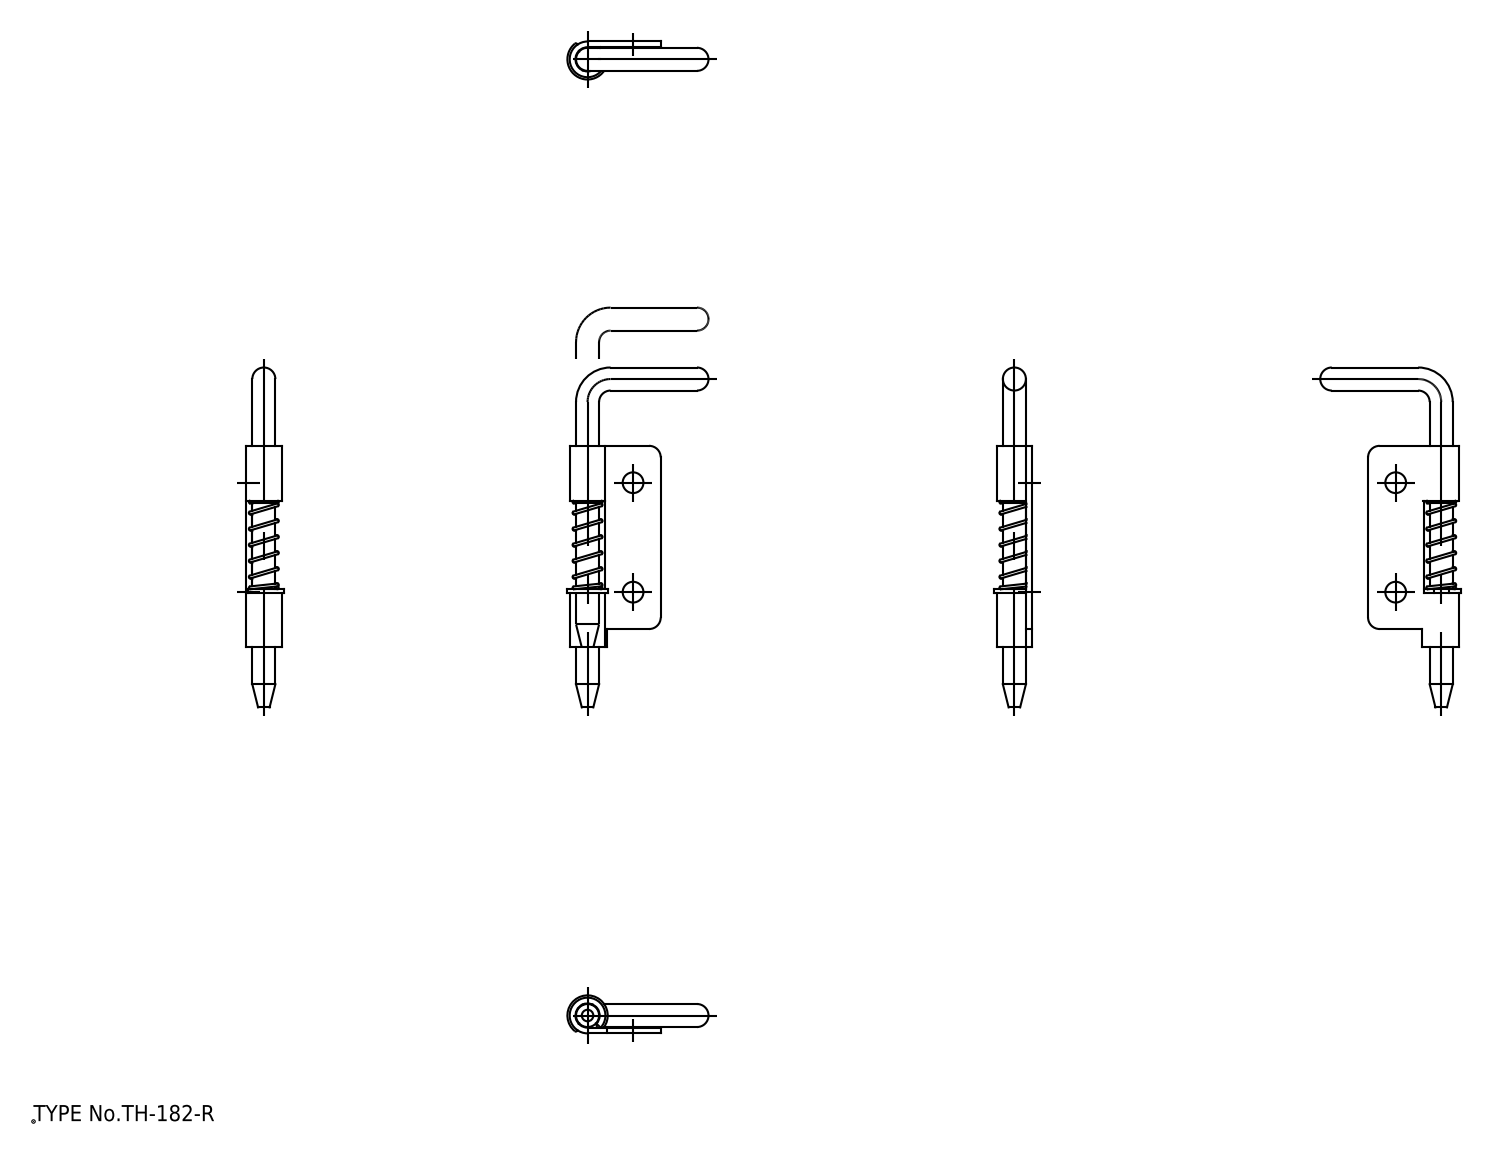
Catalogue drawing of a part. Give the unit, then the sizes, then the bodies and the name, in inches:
Units: inches
Overall size (bounding box): 2.323 × 0.965 × 0.26
Round holes (diameter × count): ⌀0.142 ×2, ⌀0.165 ×1
Round bosses / shafts (diameter × count): ⌀0.157 ×2, ⌀0.244 ×1, ⌀0.12 ×1
Partial cylindrical surfaces — rounded edges, fillets, slot ends (radius × count): R0.01 ×6, R0.079 ×2, R0.102 ×1, R0.138 ×1
Main face-to-face distances: 0.039, 1.004, 0.374, 0.024, 0.98, 0.398, 1.378, 0.63, 0.606, 0.382
Hole centre spacings: 0.748
Volume: 0.096 in³ · Surface area: 4.002 in²
Bodies: 3 solids, 87 faces (27 planar, 27 cylindrical, 33 other)
Part name (STEP PRODUCT): シャフト; スプリング_M2; ヒンジピース
STEP written by: spGate 19.8.4 (****-****-****-****) (AUTOMOTIVE_DESIGN)
